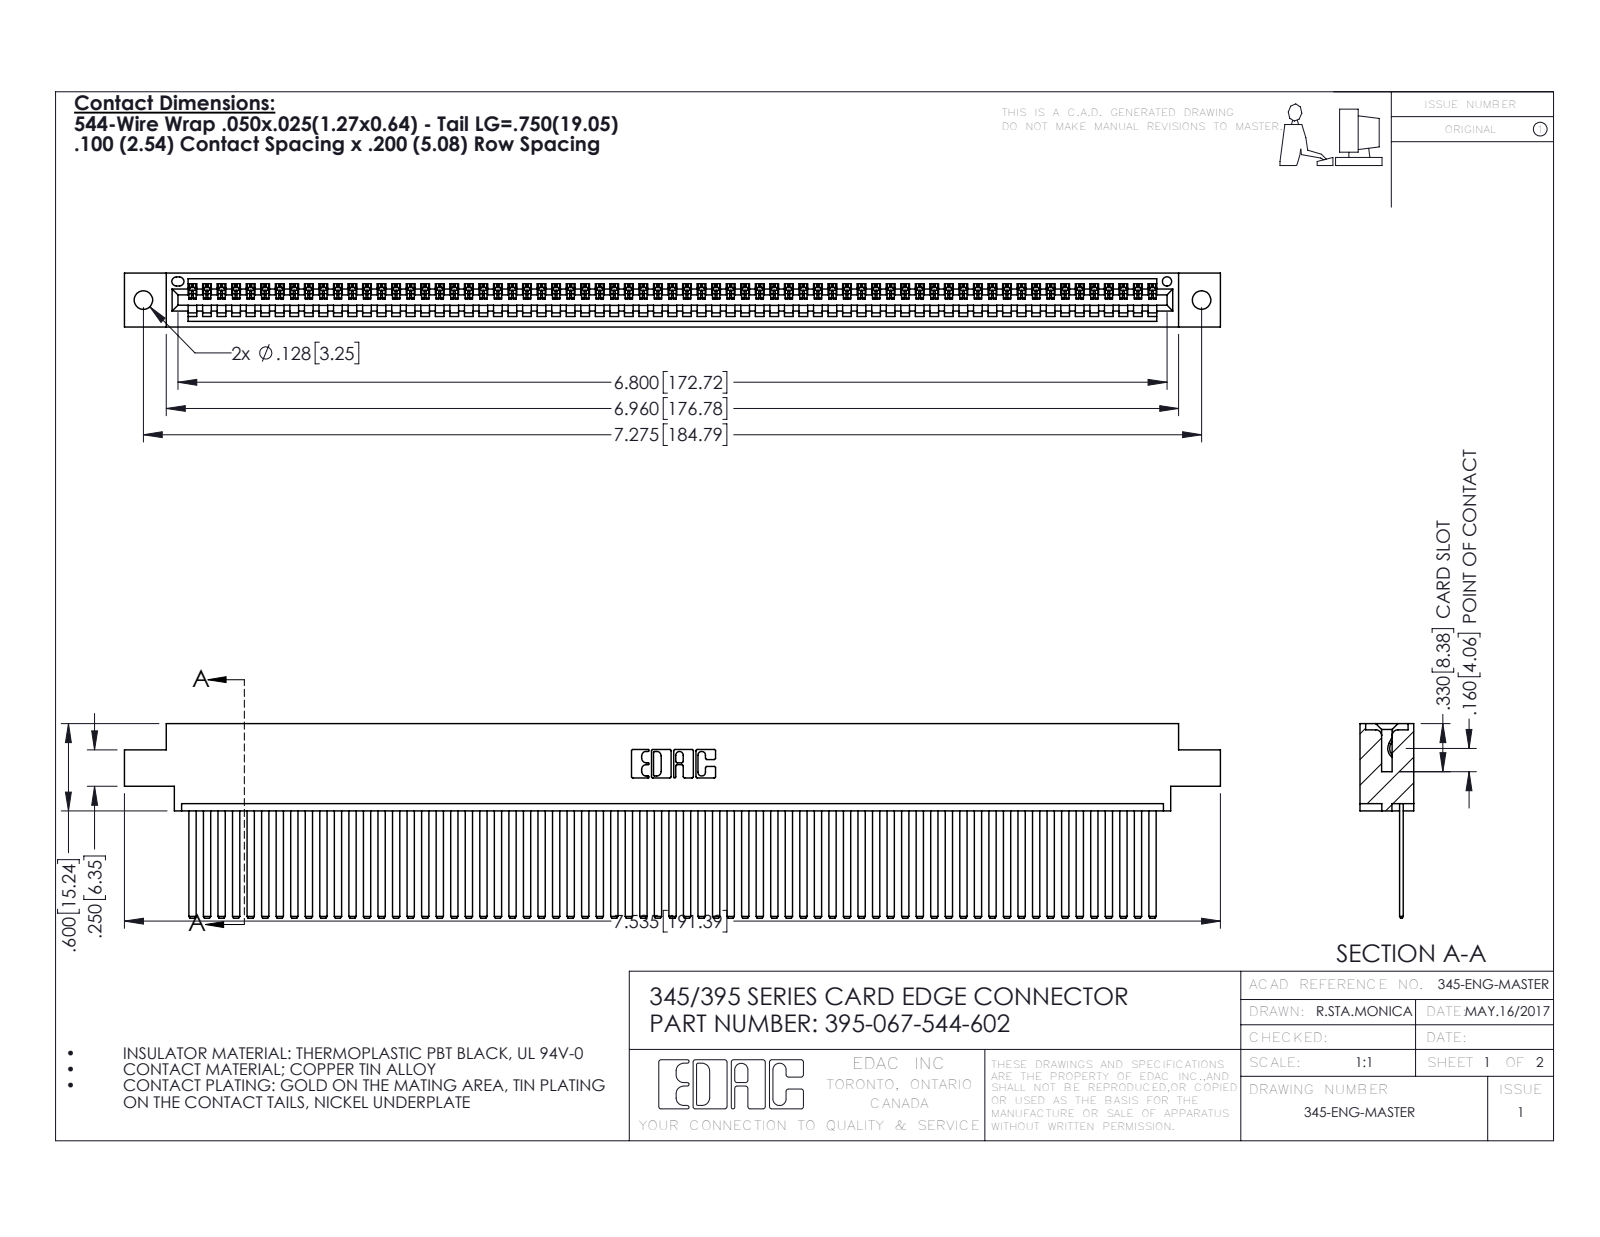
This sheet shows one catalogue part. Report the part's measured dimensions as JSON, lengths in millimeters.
{"part_name": "345 Part_0.170 Offset - 0.128 Dia; 345-292-001_345-293-144; 395-067-544-602", "step_written_by": "SolidWorks 2016 (CONFIG_CONTROL_DESIGN)", "units": "millimeters", "bodies": {"solids": 68, "faces": 3614, "planar": 2496, "cylindrical": 1118, "other": 0}, "overall_size": [191.4, 34, 9.4], "volume_mm3": 19010, "surface_area_mm2": 27790, "round_holes": [[3.3, 2], [1.6, 1]], "partial_cylinders_radius": [[0.2, 134], [0.3, 22], [0.2, 6], [0.8, 6], [0.7, 3], [0.8, 2], [1, 2], [0.4, 1]], "face_to_face_distances": [1.8, 7.6, 0.6, 2.5, 6.9, 9.4, 5.1, 5.7, 4.4, 3.8], "hole_center_spacings": [6.9, 178.8, 184.8]}
